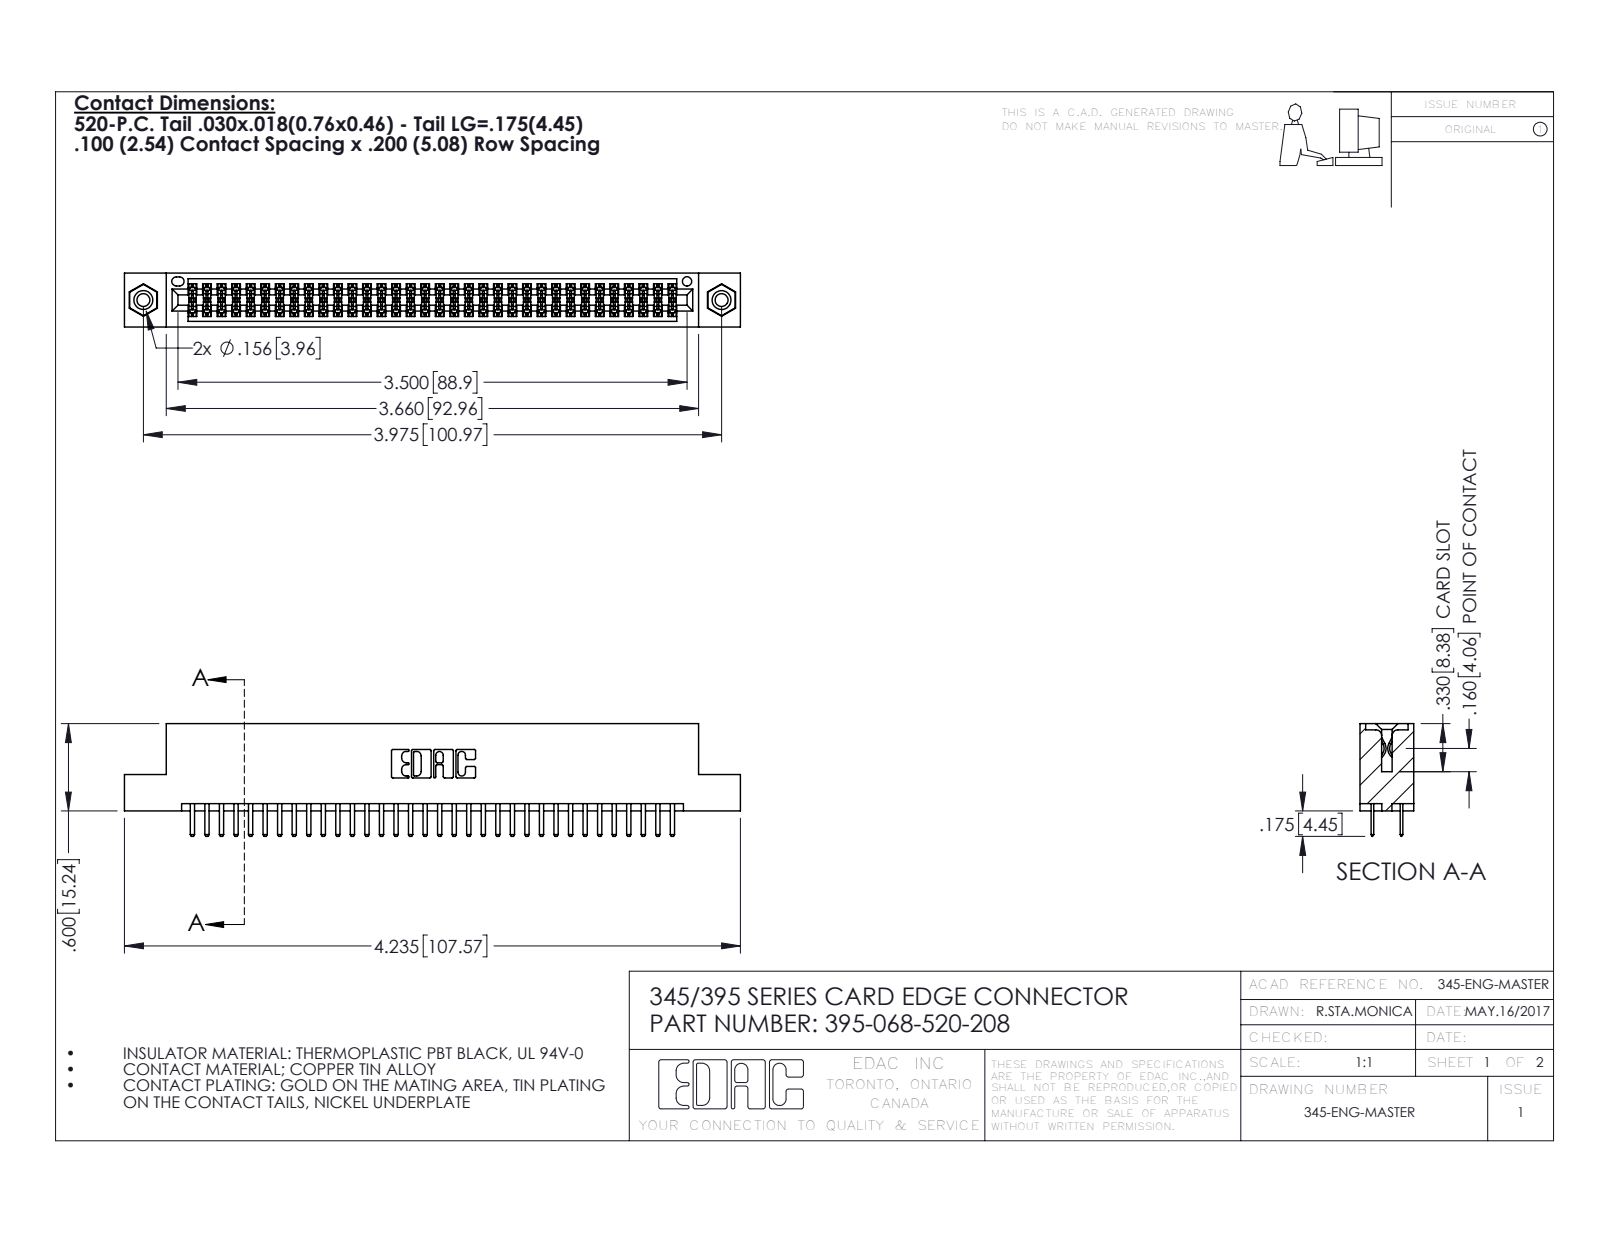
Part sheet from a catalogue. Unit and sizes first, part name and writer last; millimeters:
Units: millimetres
Overall size (bounding box): 107.6 × 19.7 × 9.4
Round holes (diameter × count): ⌀2.3 ×2, ⌀3.2 ×2, ⌀4 ×2, ⌀1.6 ×1
Round bosses / shafts (diameter × count): ⌀3.9 ×2
Partial cylindrical surfaces — rounded edges, fillets, slot ends (radius × count): R0.2 ×102, R0.3 ×72, R0.3 ×22, R0.2 ×6, R0.8 ×6, R0.7 ×3, R0.4 ×2, R0.5 ×2
Main face-to-face distances: 1.8, 7.6, 5.1, 9.4, 2.5, 6.9, 0.6, 5.7, 0.6, 1.8
Hole centre spacings: 6.9, 95, 101
Volume: 10 300 mm³ · Surface area: 15 080 mm²
Bodies: 71 solids, 3858 faces (2492 planar, 1350 cylindrical, 16 other)
Part name (STEP PRODUCT): 395-068-520-208; 345 Part_Flush Mounting Lugs - 0.156 Dia-TI; 345-292-001_345-293-120; 345-250-001_345-250-003-102
STEP written by: SolidWorks 2016 (CONFIG_CONTROL_DESIGN)
